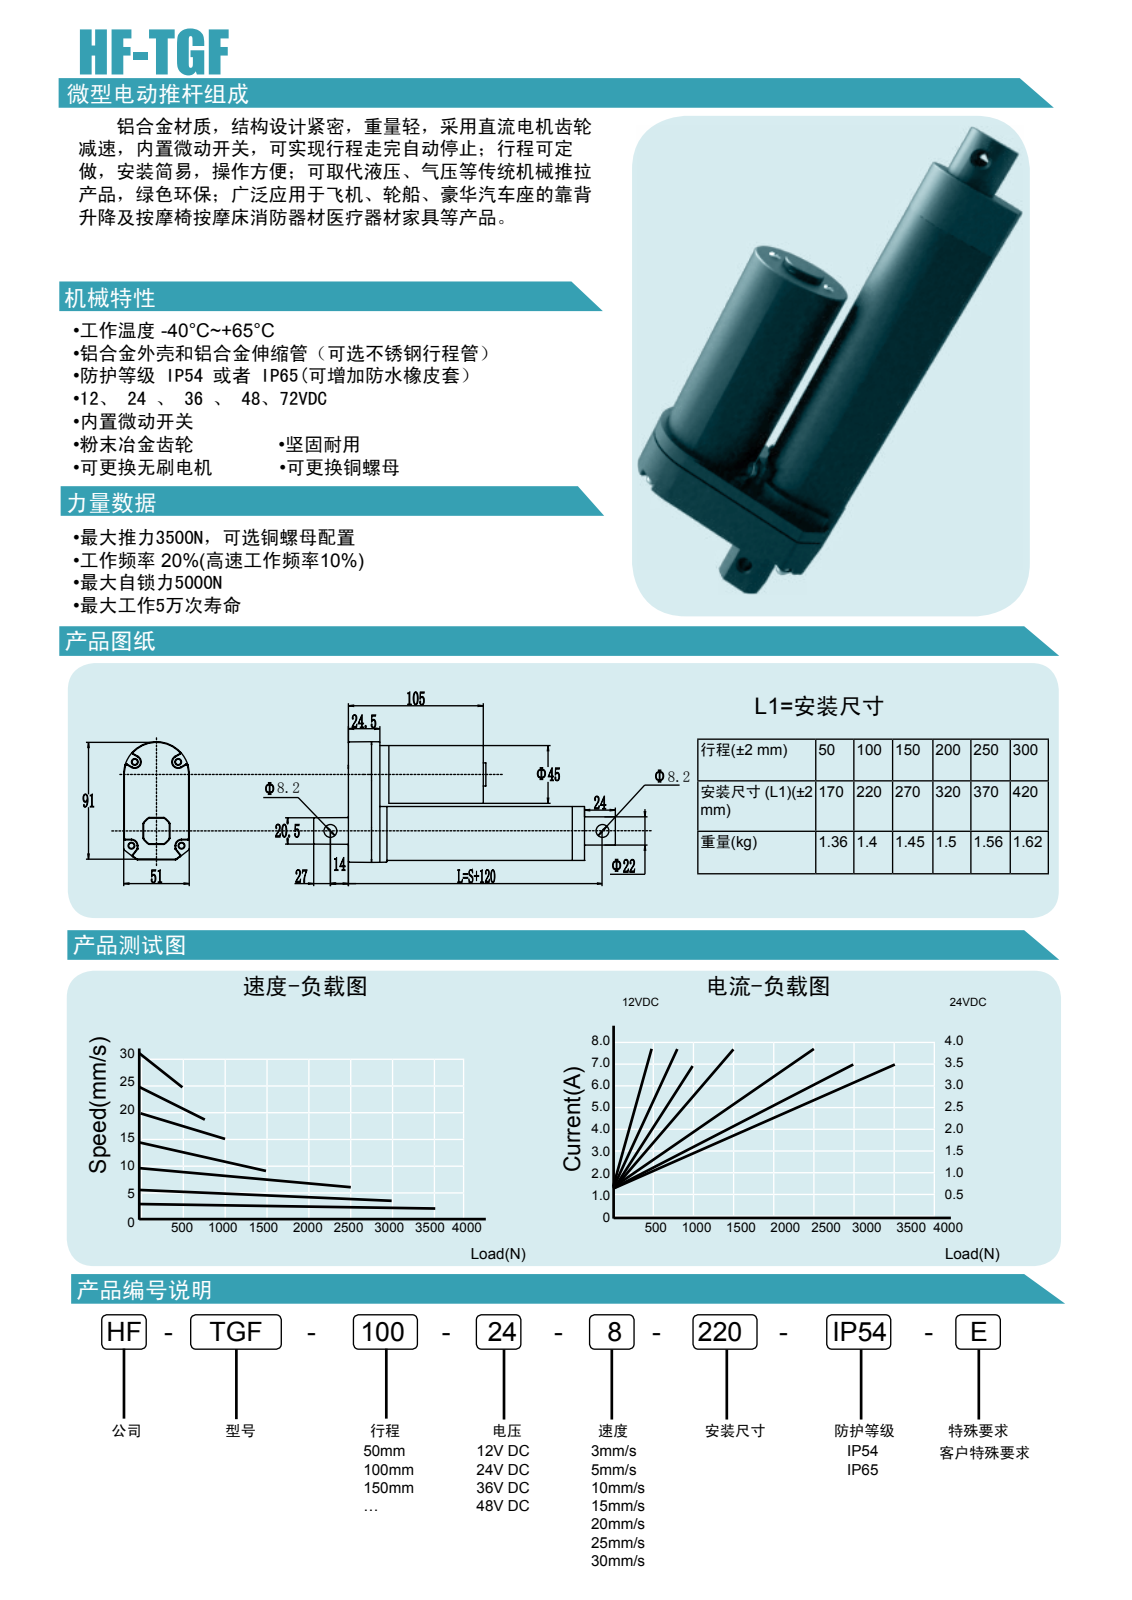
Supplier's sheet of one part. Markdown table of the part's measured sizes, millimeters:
| quantity | value |
| --- | --- |
| part name | DOWN; UP; MOTER; WAIKE (+3 more) |
| STEP written by | PRO/ENGINEER BY PARAMETRIC TECHNOLOGY CORPORATION, 2008380 (CONFIG_CONTROL_DESIGN) |
| units | millimeters |
| bodies | 6 solids, 220 faces (71 planar, 93 cylindrical, 56 other) |
| overall size | 242 × 94 × 51 |
| volume | 369 183 mm³ |
| surface area | 101 056 mm² |
| round holes (diameter × count) | 8.2 × 2, 20 × 1 |
| round bosses / shafts (diameter × count) | 51 × 1, 45 × 1, 22 × 1, 19 × 1 |
| partial cylindrical surfaces (radius × count) | 0.5 × 25, 0.5 × 8, 1 × 8, 1.5 × 4, 4.5 × 4, 1.19 × 2, 0.75 × 1, 12 × 1 |
| main face-to-face distances | 6.5, 18, 24.5, 1.97, 1.68, 1.98, 23.5, 5.5, 1, 51 |
| hole center spacings | 220 |
